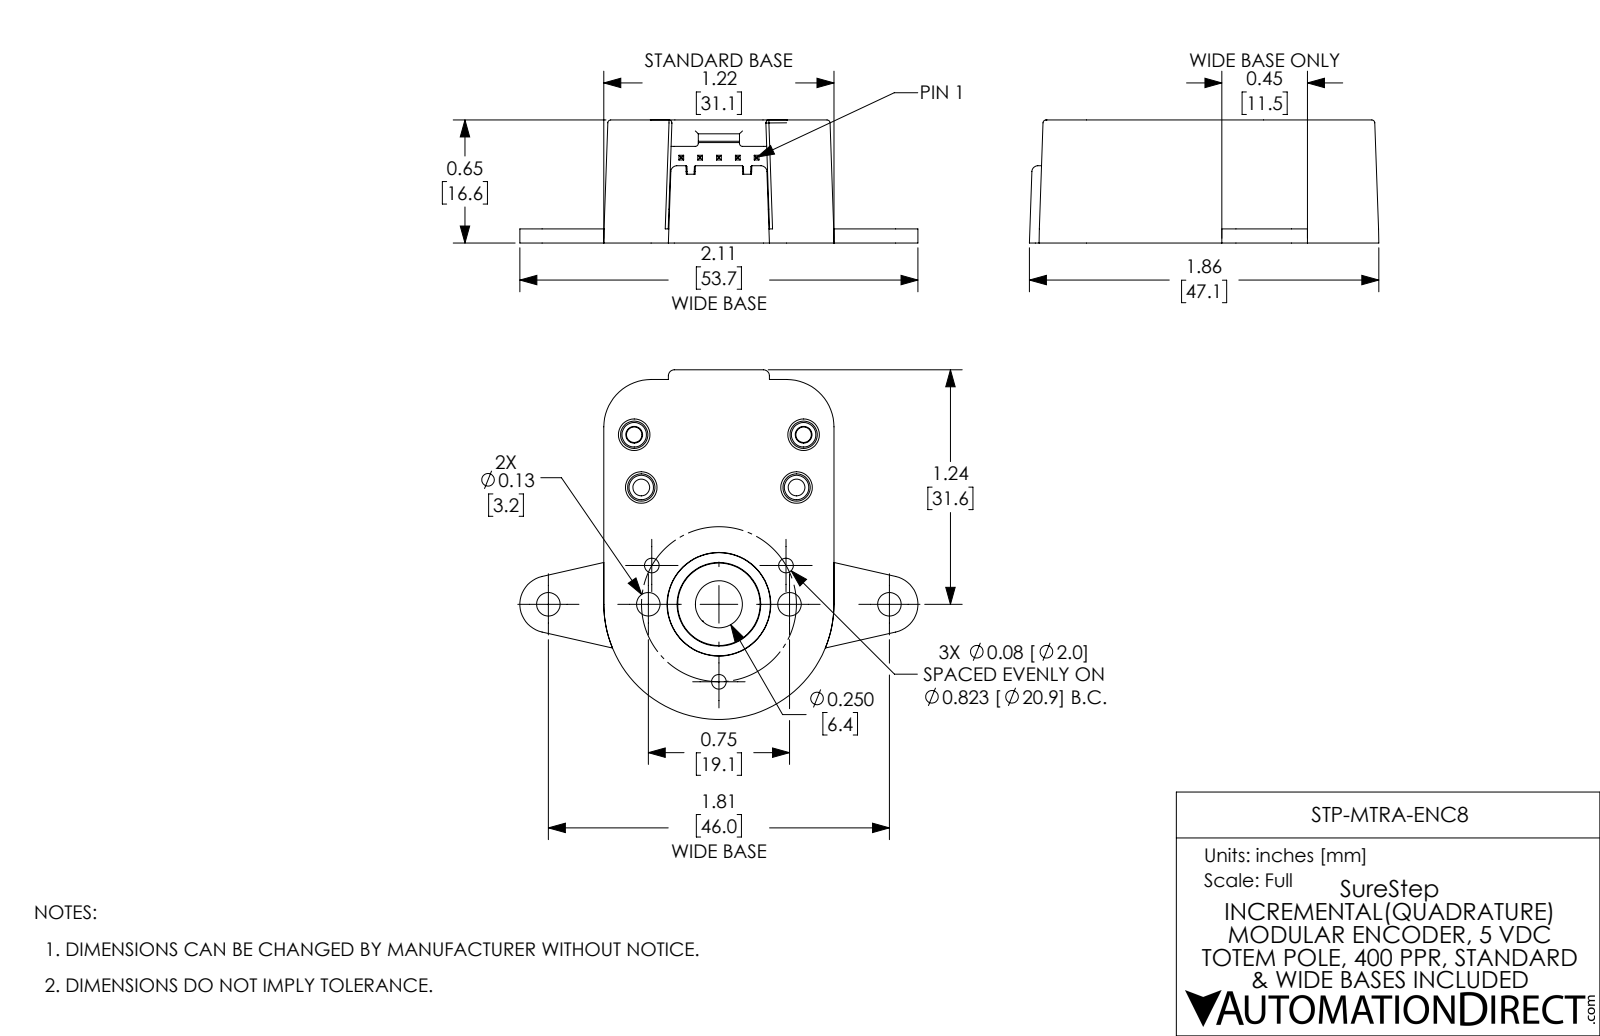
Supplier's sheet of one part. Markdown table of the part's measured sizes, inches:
| quantity | value |
| --- | --- |
| part name | STP-MTRA-ENC8 |
| STEP written by | SolidWorks 2017 (AUTOMOTIVE_DESIGN) |
| units | inches |
| bodies | 14 solids, 1349 faces (481 planar, 334 cylindrical, 534 other) |
| overall size | 3.75 × 1.865 × 0.671 |
| volume | 0.489 in³ |
| surface area | 25.74 in² |
| round holes (diameter × count) | 0.078 × 6, 0.145 × 6, 0.125 × 5, 0.089 × 4, 0.095 × 2, 0.109 × 2, 0.145 × 2, 0.093 × 1, 0.125 × 1, 0.25 × 1, 0.551 × 1 |
| round bosses / shafts (diameter × count) | 0.187 × 4, 0.16 × 4, 0.096 × 4, 0.112 × 3, 0.195 × 2, 0.52 × 1, 0.487 × 1, 0.375 × 1 |
| partial cylindrical surfaces (radius × count) | 0.016 × 36, 0.031 × 34, 0.01 × 4, 0.047 × 2, 0.047 × 2, 0.048 × 2, 0.075 × 2, 0.095 × 2 |
| main face-to-face distances | 0.019, 0.135, 0.653, 0.671, 0.154, 0.518, 0.536, 0.405, 0.117, 0.423 |
| hole center spacings | 2.081, 0.207, 0.282, 0.418, 0.557, 0.621, 0.7, 0.713 |
